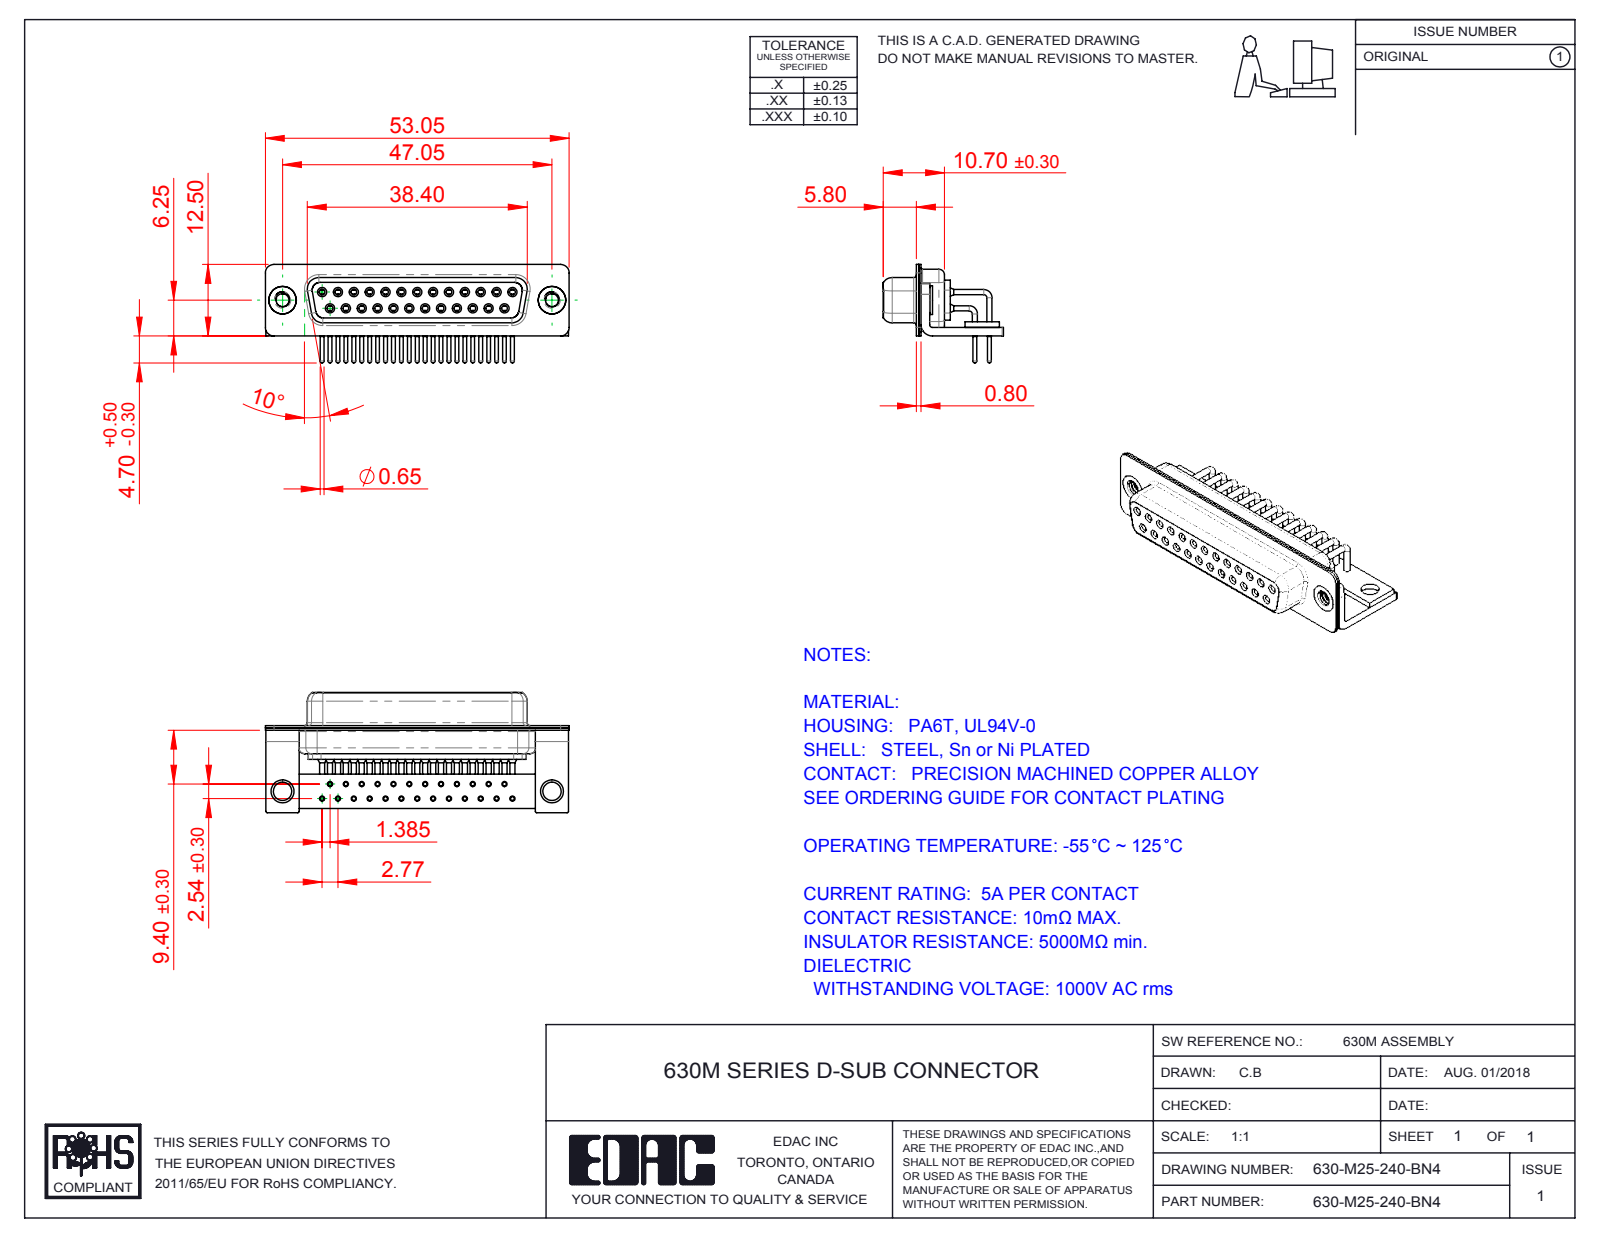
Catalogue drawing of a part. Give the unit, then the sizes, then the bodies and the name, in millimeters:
Units: millimetres
Overall size (bounding box): 53.05 × 21 × 17.2
Round holes (diameter × count): ⌀0.9 ×25, ⌀1 ×25, ⌀1.1 ×25, ⌀1.7 ×25, ⌀1.8 ×25, ⌀2 ×25, ⌀2.26 ×2, ⌀3.2 ×2, ⌀4 ×2, ⌀4.8 ×2
Round bosses / shafts (diameter × count): ⌀1.6 ×25, ⌀1.5 ×25, ⌀0.9 ×25, ⌀0.65 ×25, ⌀5 ×2, ⌀4.9 ×2
Partial cylindrical surfaces — rounded edges, fillets, slot ends (radius × count): R0.25 ×16, R1.5 ×16, R2 ×13, R1.35 ×10, R1.6 ×8, R0.5 ×5, R0.6 ×4, R0.65 ×4
Main face-to-face distances: 0.4, 2.3, 1.9, 1.45, 8.95, 0.85, 9.35, 0.8, 6.2, 1
Hole centre spacings: 2.77, 5.54, 8.31, 11.08, 13.85, 3.16, 4.87, 16.62
Volume: 4 451 mm³ · Surface area: 11 099 mm²
Bodies: 33 solids, 1704 faces (468 planar, 784 cylindrical, 452 other)
Part name (STEP PRODUCT): 630M Stabilizer Board_25 Contacts; 630M Stabilizer Bracket; 630M 4-40 Threaded Rivet_Stabilizer; 630M Contact Row 2 (+5 more)
STEP written by: SolidWorks 2016 (CONFIG_CONTROL_DESIGN)
